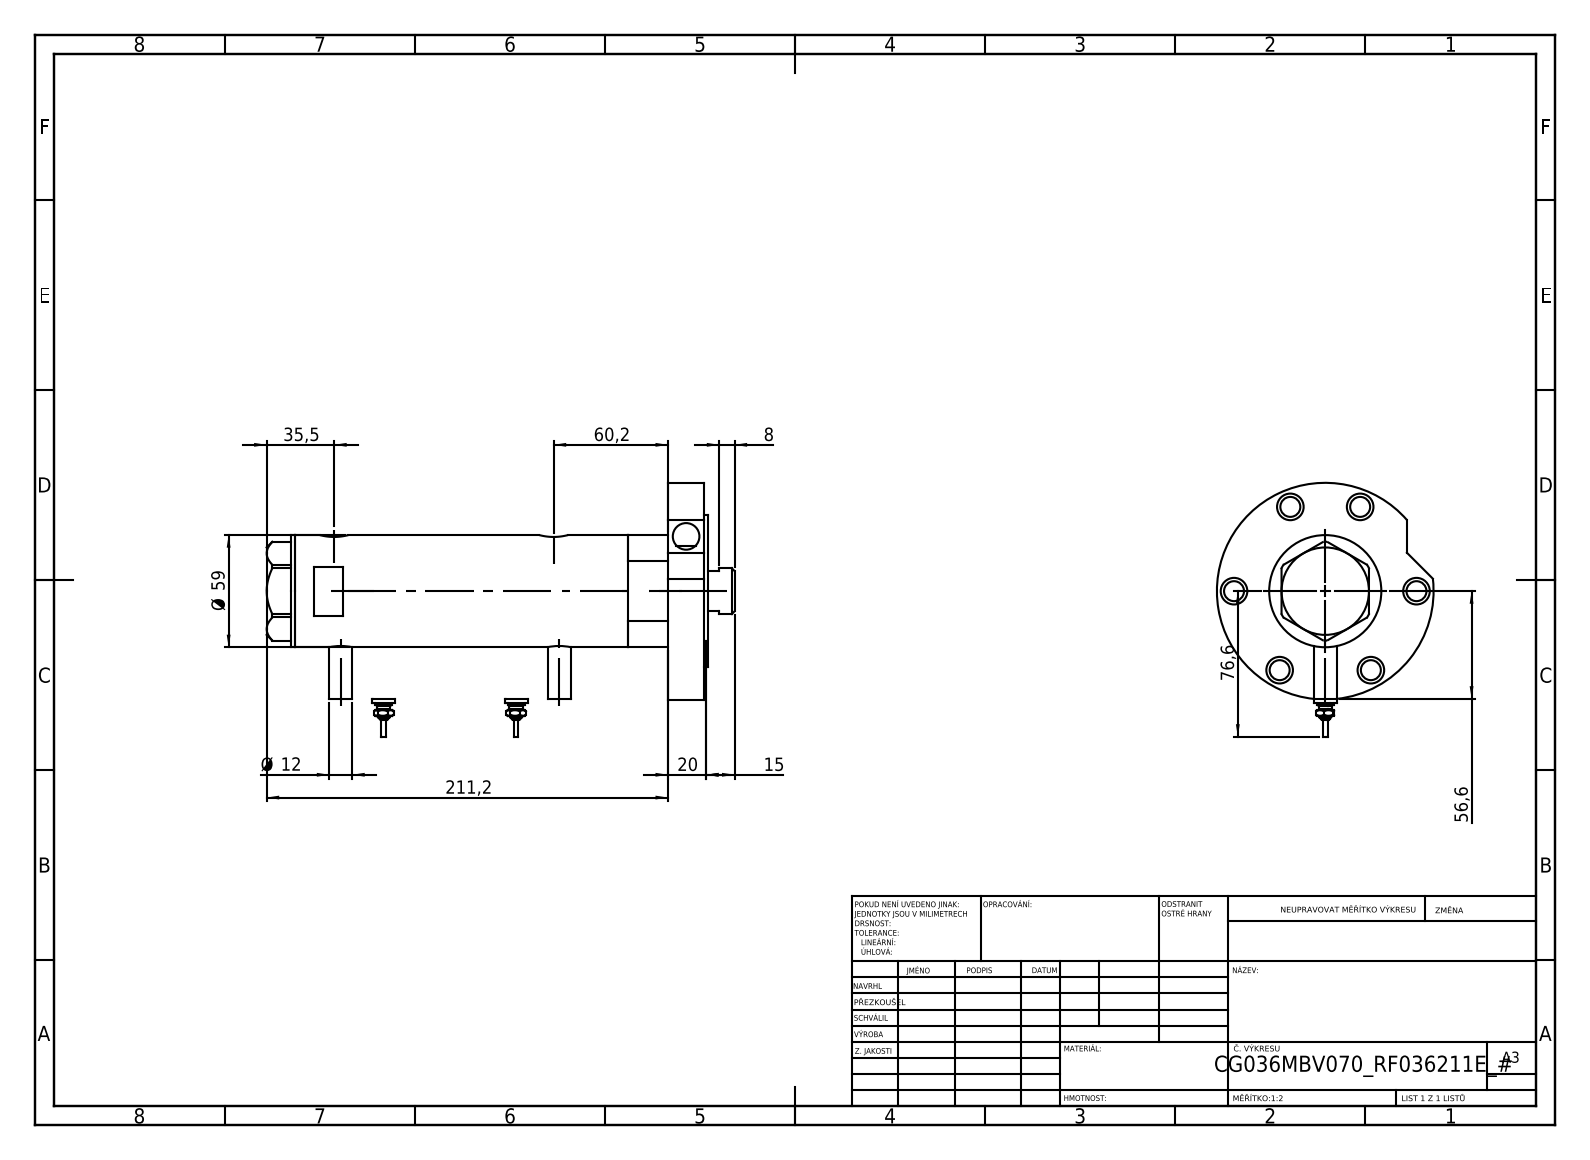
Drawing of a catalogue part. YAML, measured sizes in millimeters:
part_name: "V270CG_MIDDLE; V270CG_BACK; V270CG_VC; Switch (+2 more)"
step_written_by: "SolidWorks 2019 (CONFIG_CONTROL_DESIGN)"
units: millimeters
bodies: {solids: 7, faces: 256, planar: 90, cylindrical: 102, other: 64}
overall_size: [246.2, 133.6, 114]
volume: 705789
surface_area: 149938
round_holes:
  - {diameter: 14, count: 7}
  - {diameter: 10.5, count: 6}
  - {diameter: 9.73, count: 2}
  - {diameter: 12.5, count: 2}
  - {diameter: 15, count: 2}
  - {diameter: 8.5, count: 1}
  - {diameter: 25, count: 1}
  - {diameter: 26.5, count: 1}
  - {diameter: 36, count: 1}
  - {diameter: 40, count: 1}
  - {diameter: 48, count: 1}
  - {diameter: 52, count: 1}
round_bosses_or_shafts:
  - {diameter: 12, count: 4}
  - {diameter: 9, count: 2}
  - {diameter: 7, count: 2}
  - {diameter: 4.5, count: 2}
  - {diameter: 2.5, count: 2}
  - {diameter: 114, count: 1}
  - {diameter: 80, count: 1}
  - {diameter: 59, count: 1}
face_to_face_distances: [2, 19, 21, 217.2, 196.2, 215.2, 137.2, 59, 78, 80]
hole_center_spacings: [48, 53.34, 79.82, 83.14, 86.1, 95.8, 2.9, 3.5]
